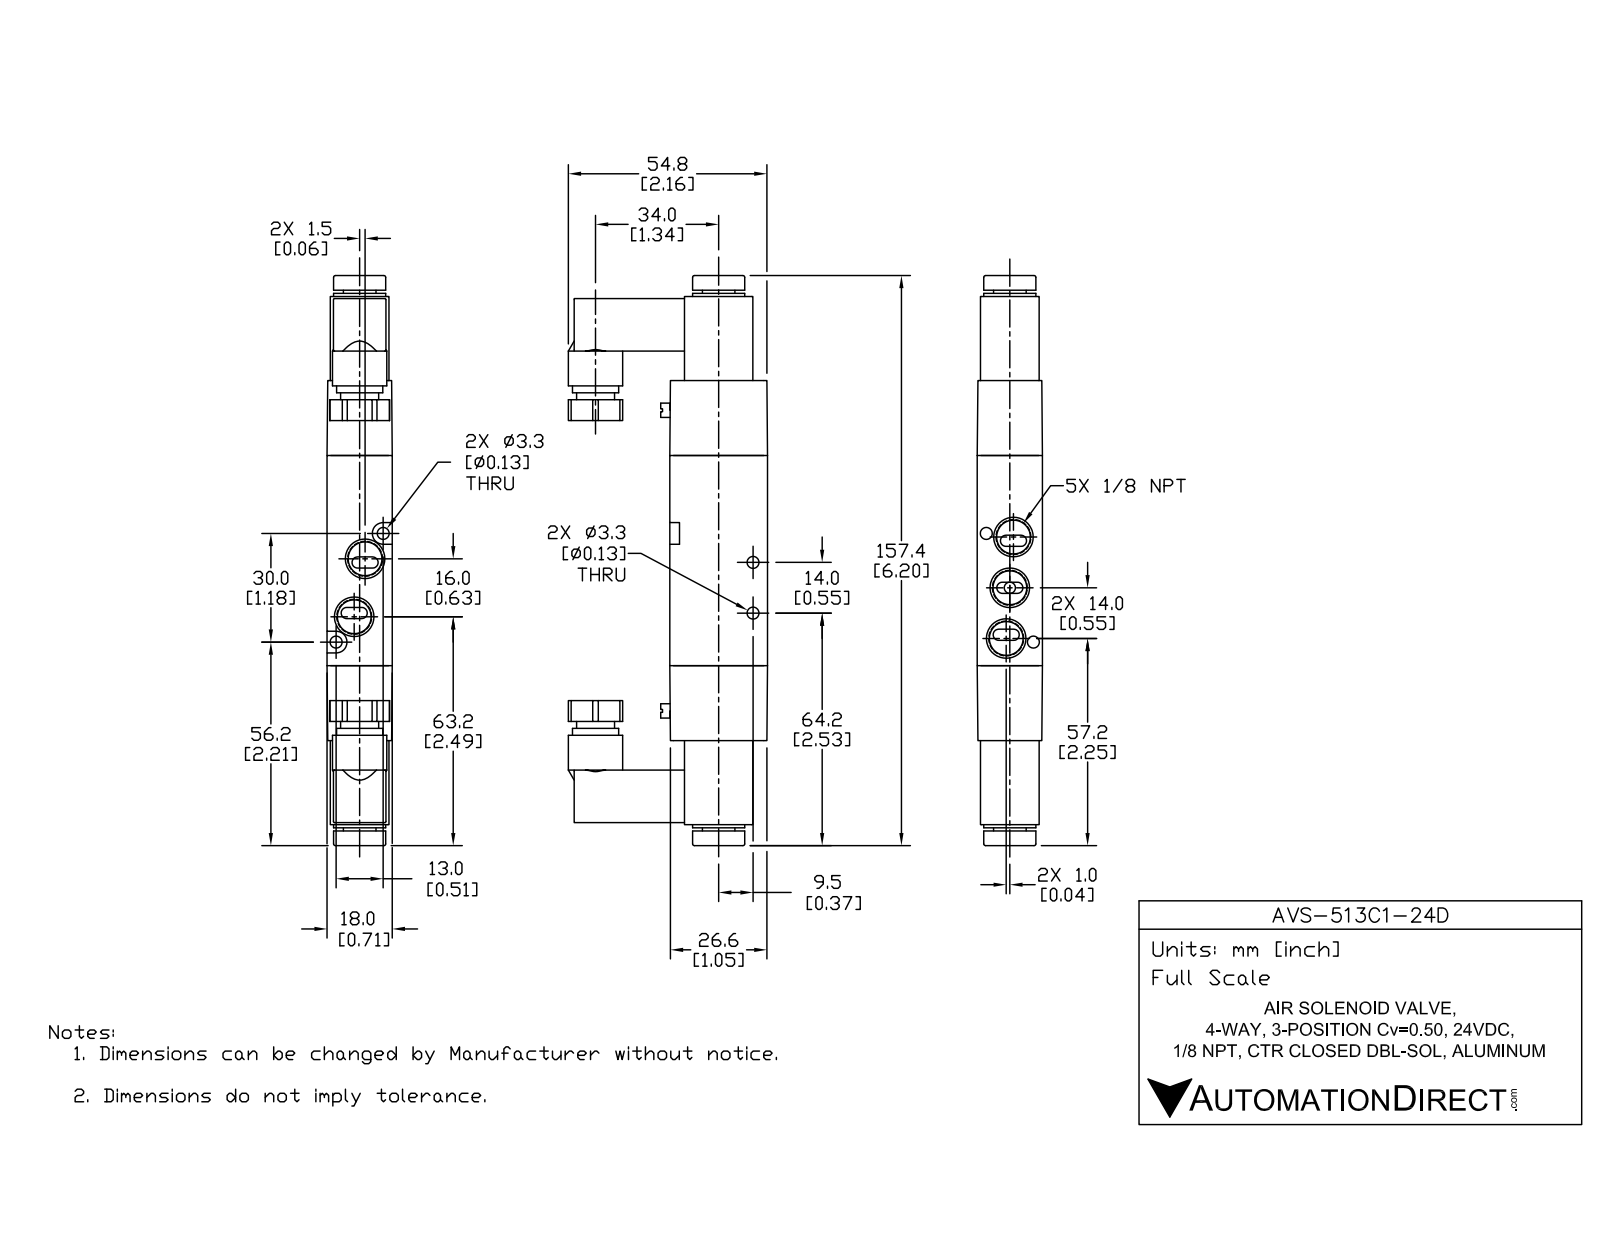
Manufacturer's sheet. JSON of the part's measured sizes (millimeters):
{"part_name": "AVS-513C1-24D", "step_written_by": "SolidWorks 2021 (CONFIG_CONTROL_DESIGN)", "units": "millimeters", "bodies": {"solids": 5, "faces": 246, "planar": 131, "cylindrical": 91, "other": 24}, "overall_size": [157.4, 55, 18], "volume_mm3": 77332, "surface_area_mm2": 24997, "round_holes": [[8.43, 5], [3.2, 2], [3.3, 2], [9.3, 1]], "round_bosses_or_shafts": [[6.8, 2], [15, 1], [14.4, 1], [12.8, 1], [10.5, 1], [9, 1]], "partial_cylinders_radius": [[1.54, 10], [0.3, 8], [0.5, 8], [1, 8], [3, 2]], "face_to_face_distances": [1.75, 16.25, 18.21, 0.31, 14.5, 18, 23.66, 18.52, 58, 3.86], "hole_center_spacings": [7.57, 14.04, 16.35, 29.52, 6.25, 6.82, 8.04, 8.19]}
